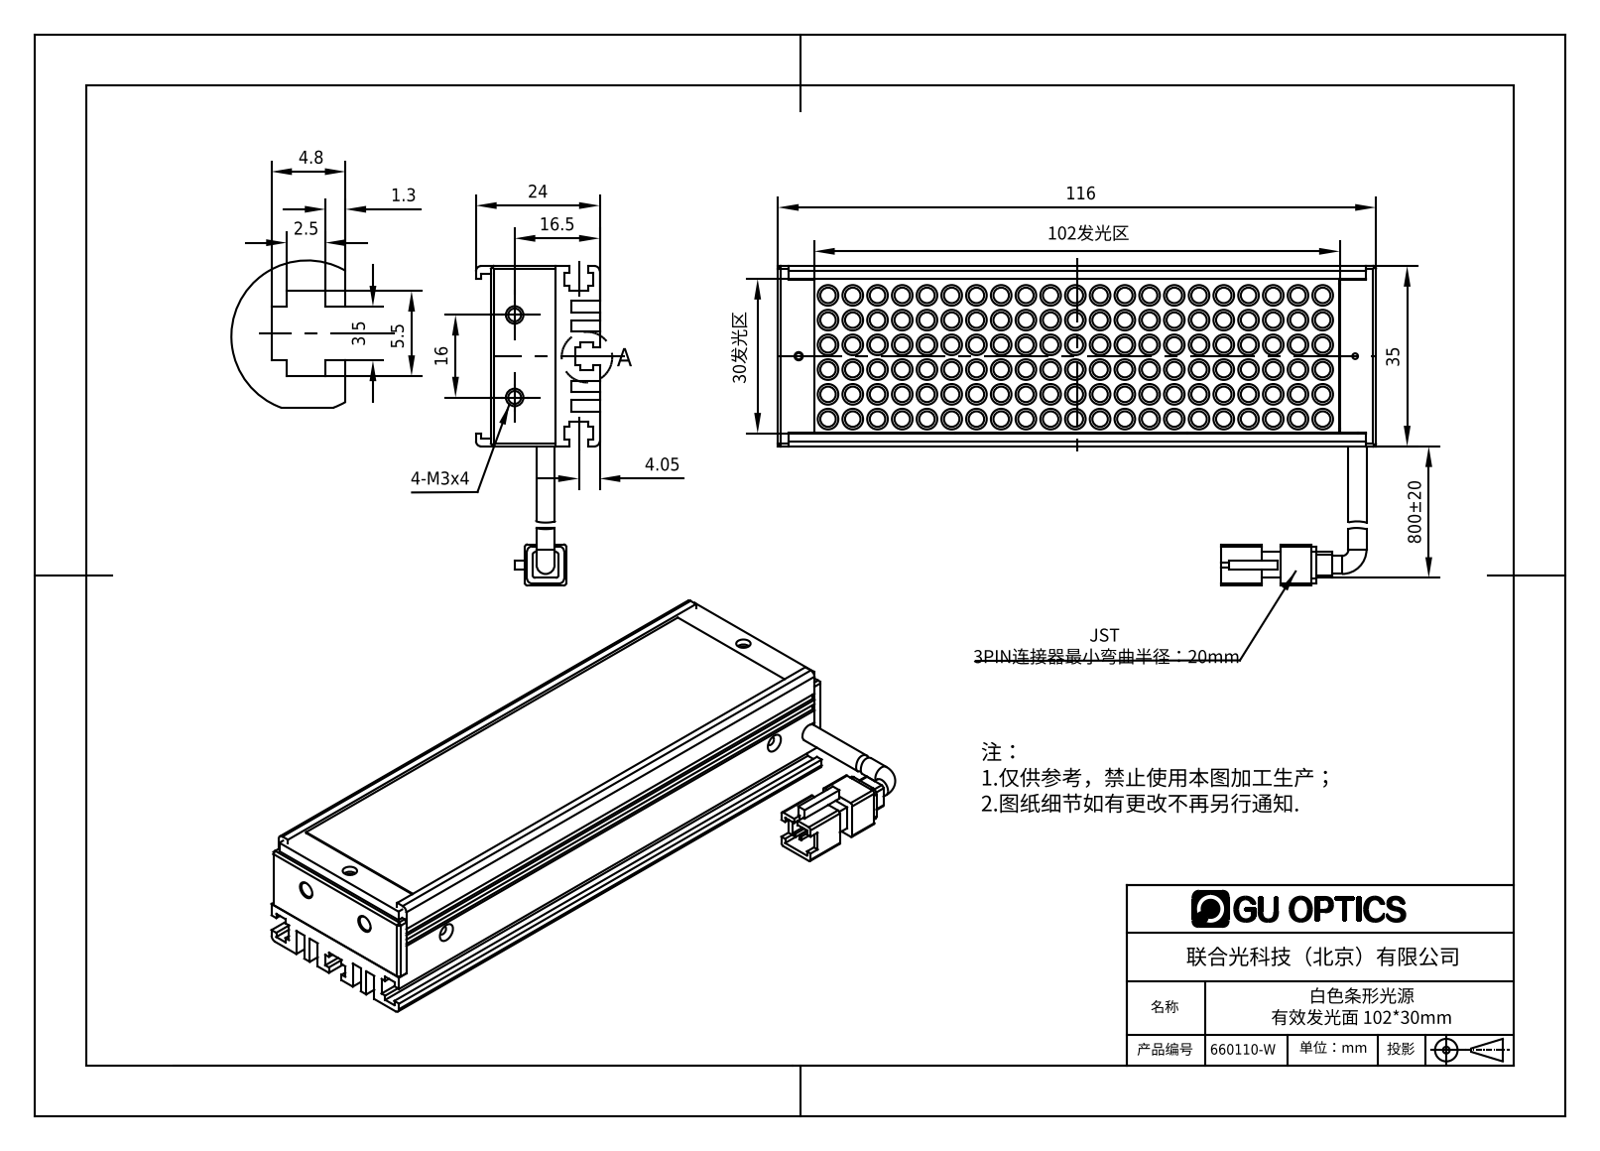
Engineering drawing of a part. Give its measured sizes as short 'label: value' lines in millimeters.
name: 660110-W
written by: SolidWorks 2016 (AUTOMOTIVE_DESIGN)
unit: mm
bodies: 8 solids, 1209 faces (393 planar, 587 cylindrical, 229 other)
size: 116 × 62 × 24
volume: 53 726 mm³; area: 60 118 mm²
holes: 5× ⌀1.6, 2× ⌀1.5, 2× ⌀1.7, 2× ⌀2.5, 2× ⌀2.8, 2× ⌀3, 1× ⌀1.1, 1× ⌀1.25, 1× ⌀2
bosses: 126× ⌀4, 126× ⌀3, 2× ⌀3.5
rounds: 12× R1, 8× R0.5, 1× R1.65
face distances: 2, 2.2, 8.6, 1, 2.5, 12.6, 14.6, 9, 4, 7
hole spacings: 108, 7, 9.14, 10.5, 99.01, 99.15, 108.23, 16
